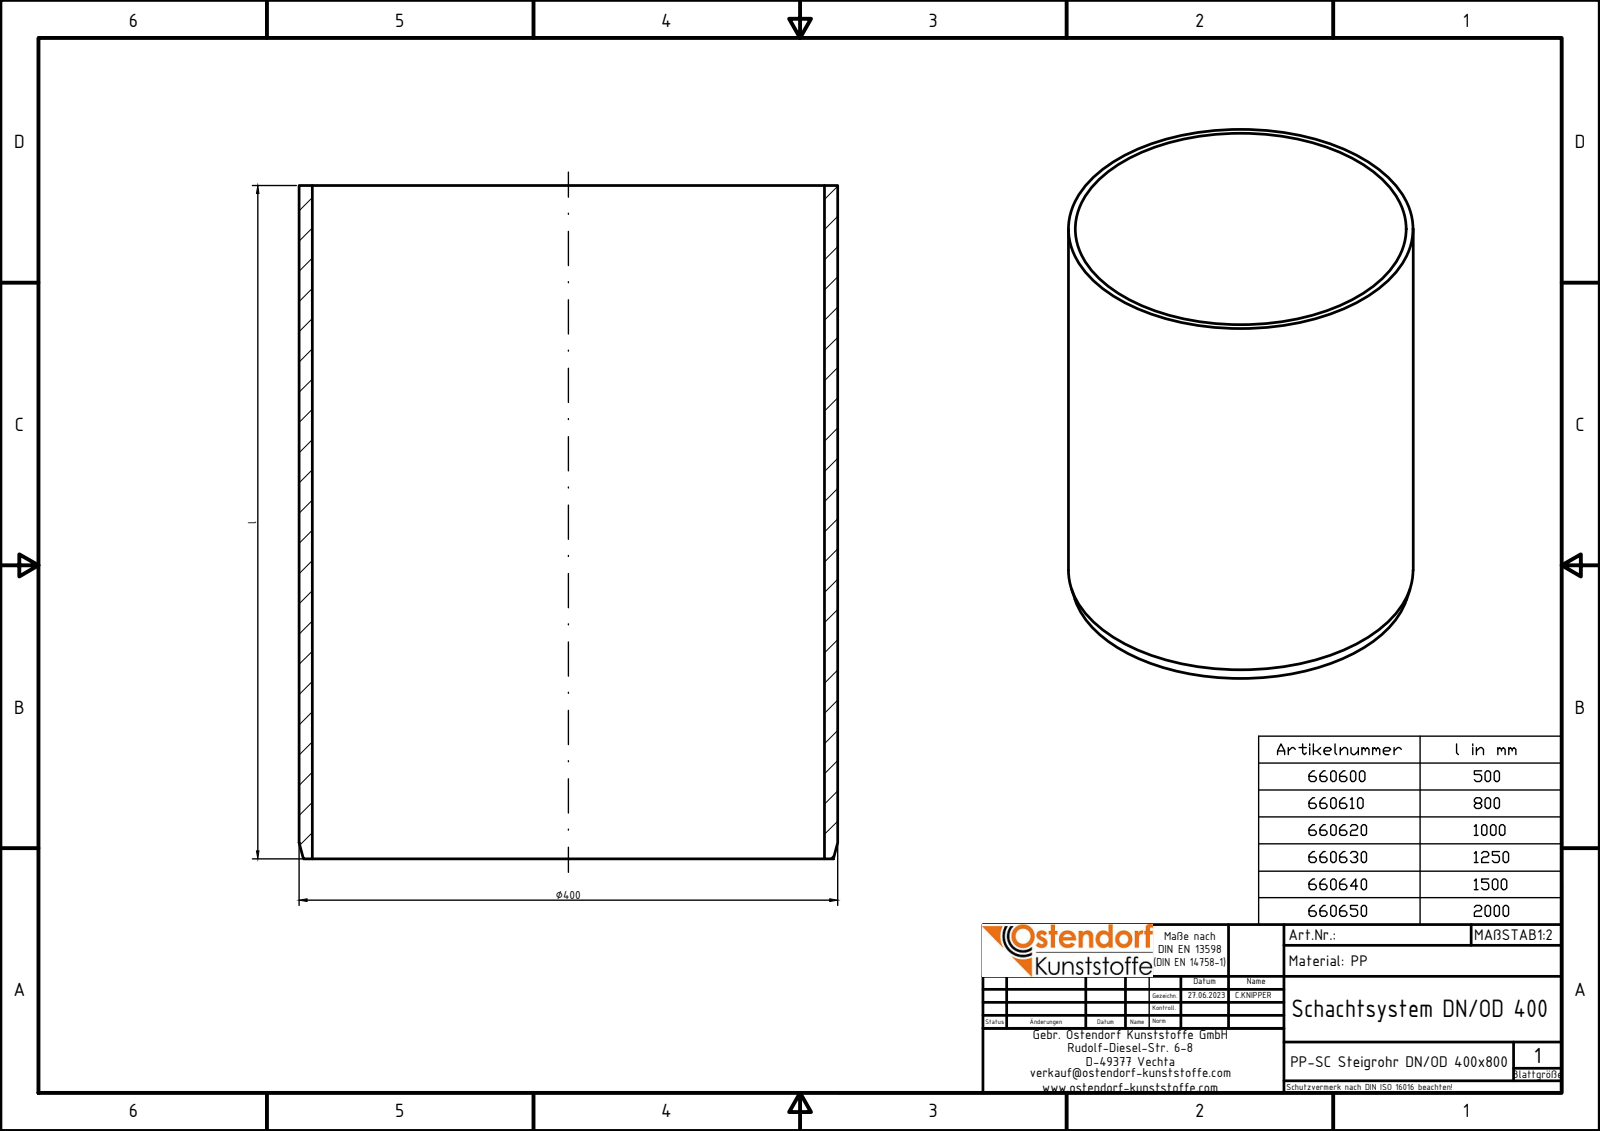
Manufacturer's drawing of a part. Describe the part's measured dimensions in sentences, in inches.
The part is named "660610". Its 3-D file was written by "Autodesk Inventor 2020 (AUTOMOTIVE_DESIGN)". It is 1 solid with 5 faces: 2 planar, 2 cylindrical and 1 other. Overall it measures 31.496 by 15.748 by 15.748 inches. Its volume is 585 cubic inches and its surface area 3 072 square inches. Round holes: 1 of diameter 14.976. Round bosses or shafts: 1 of diameter 15.748. The main face-to-face distances are 31.496.
